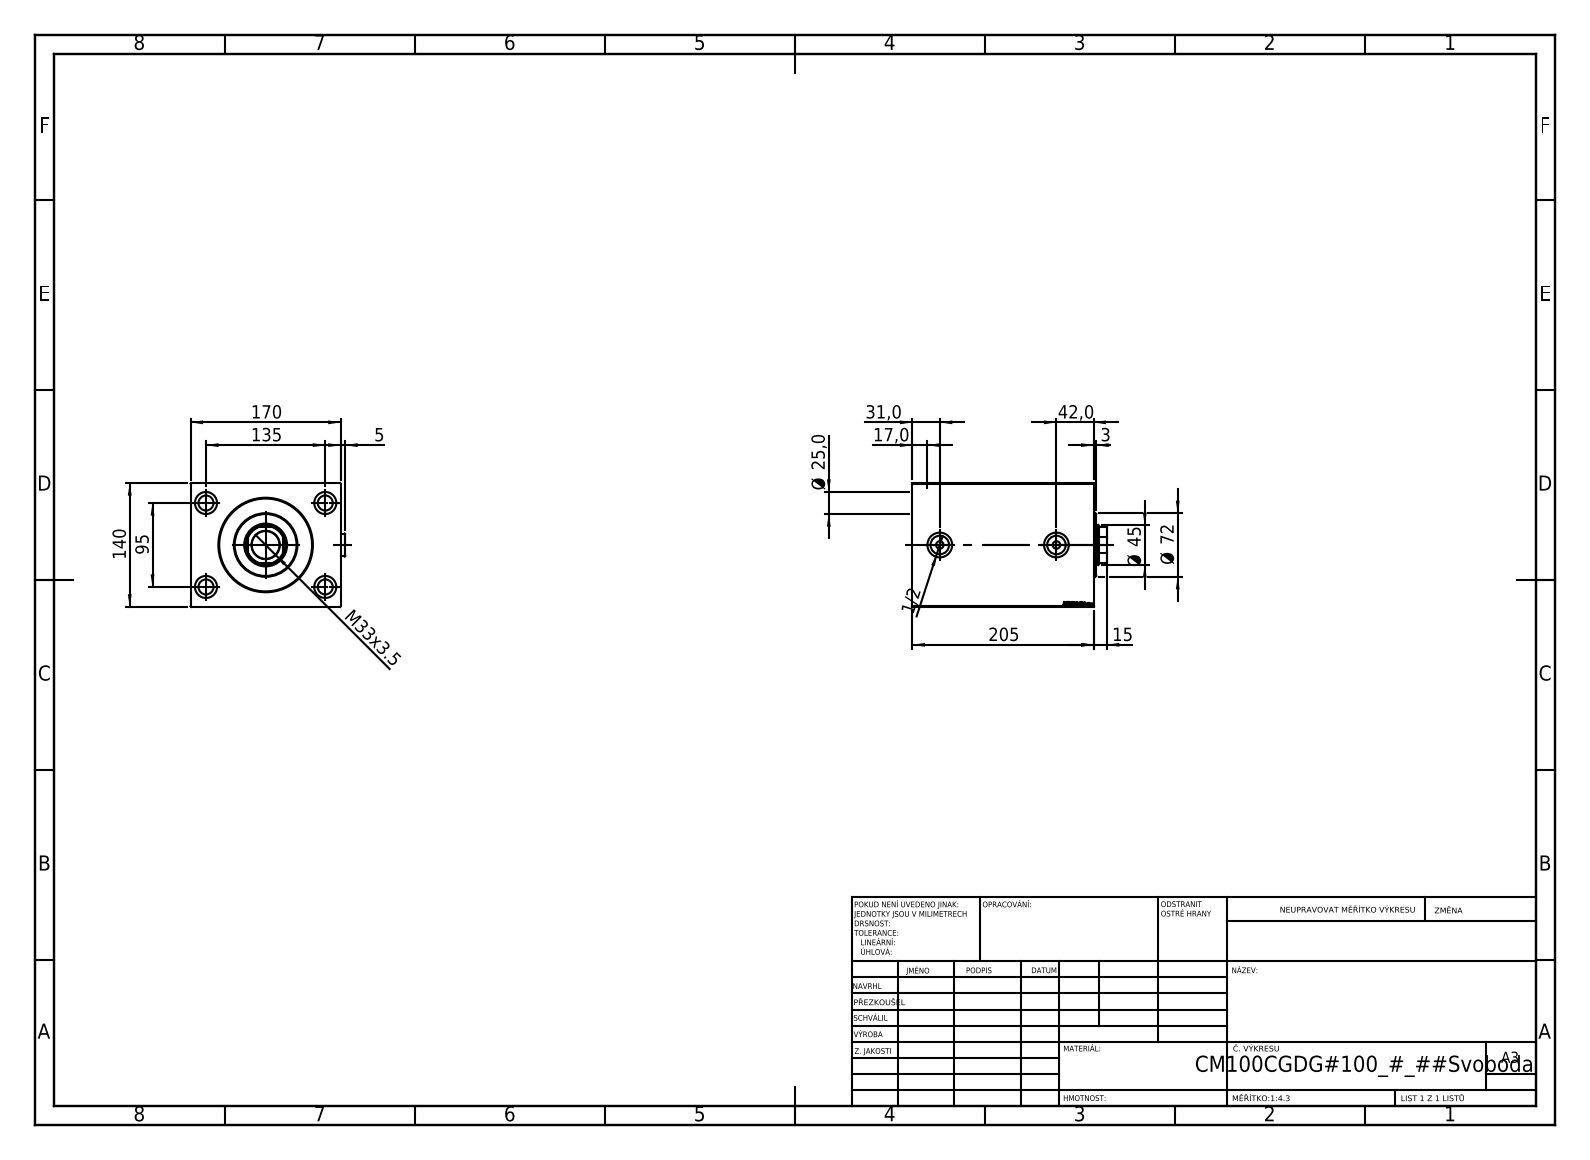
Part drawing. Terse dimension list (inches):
name: V450CM_C_VCP; V450CM_VC_B; Zatka_OIL_PORT; V450CM_C_Body
written by: SolidWorks 2019 (CONFIG_CONTROL_DESIGN)
unit: in
bodies: 5 solids, 919 faces (443 planar, 78 cylindrical, 398 other)
size: 8.661 × 6.886 × 5.512
volume: 244.6 in³; area: 565.2 in²
holes: 4× ⌀0.669, 4× ⌀0.984, 2× ⌀0.335, 2× ⌀0.825, 2× ⌀1.102, 1× ⌀1.24, 1× ⌀1.772, 1× ⌀1.909, 1× ⌀3.937, 1× ⌀4.016, 1× ⌀4.134
bosses: 2× ⌀1.024, 1× ⌀2.835
rounds: 1× R0.866
face distances: 5.512, 6.693, 8.071, 7.047, 1.024, 0.591, 6.457, 7.48, 3.543, 3.937
hole spacings: 3.25, 3.74, 5.315, 6.499, 5.197
